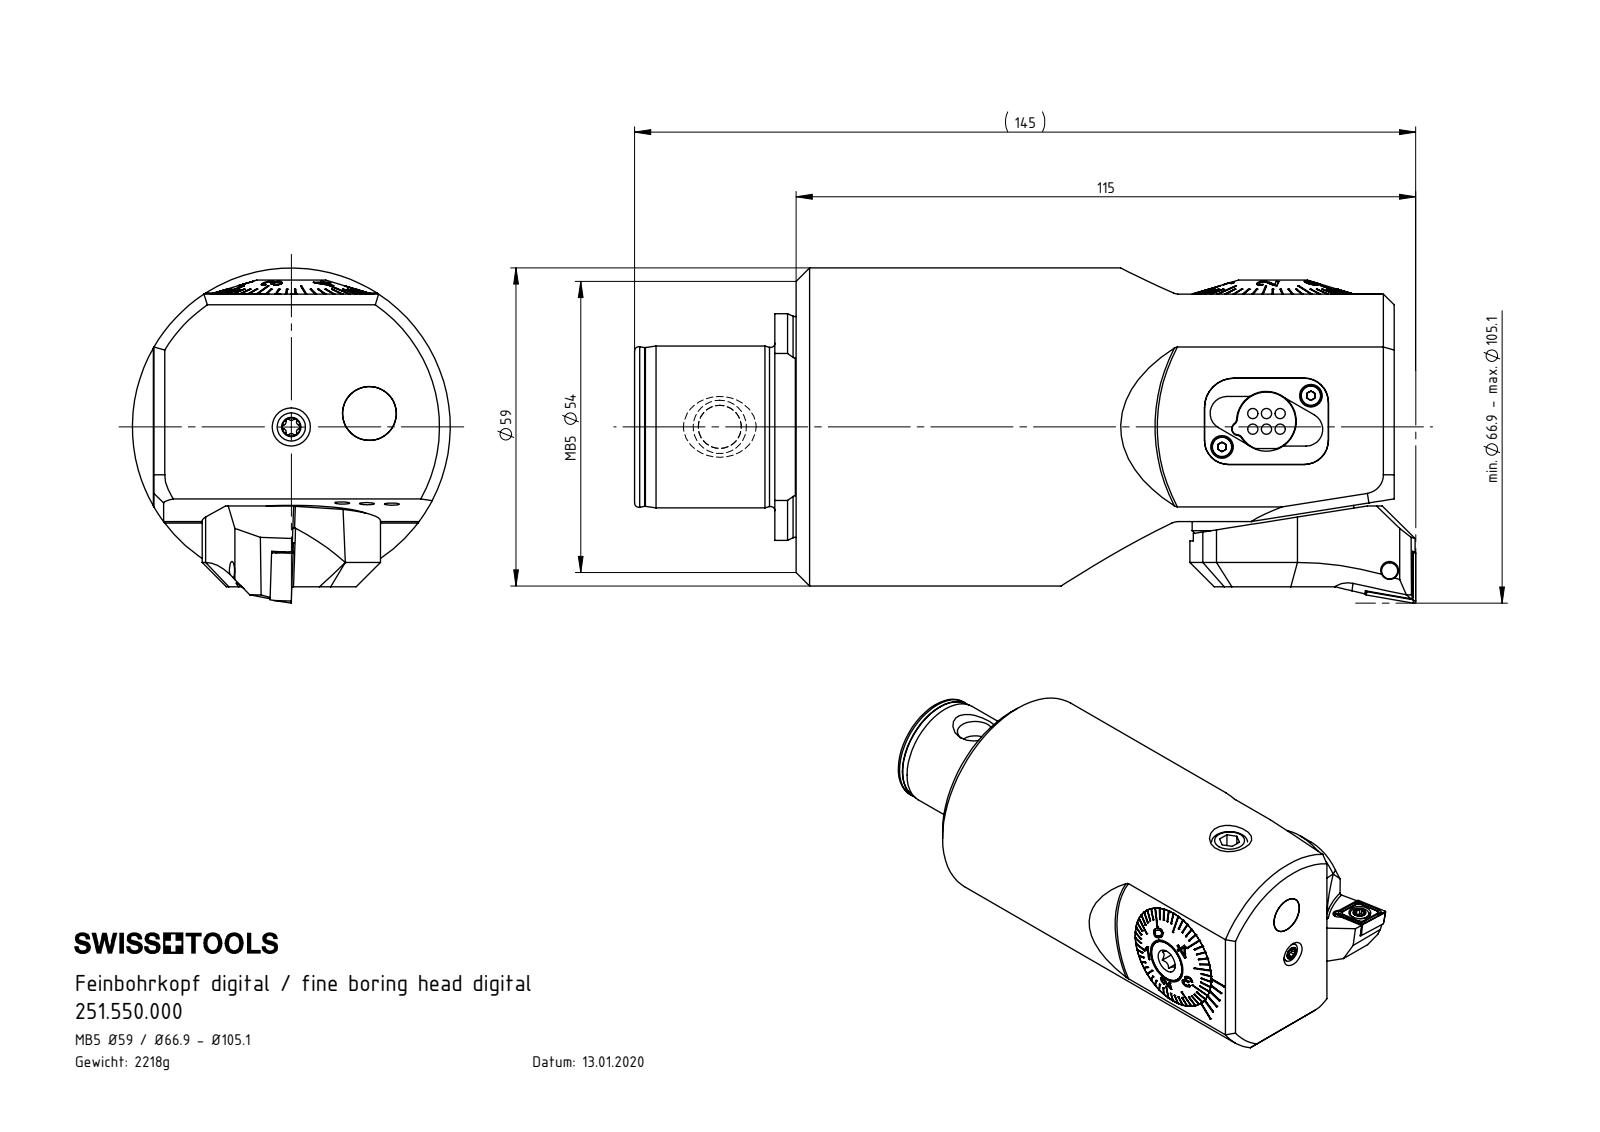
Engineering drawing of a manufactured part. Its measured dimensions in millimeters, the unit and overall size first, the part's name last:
Units: millimetres
Overall size (bounding box): 145 × 65.75 × 55
Round holes (diameter × count): ⌀3.3 ×9, ⌀4.2 ×3, ⌀8.5 ×3, ⌀1.6 ×2, ⌀2.2 ×2, ⌀8 ×2, ⌀4.4 ×1, ⌀5 ×1, ⌀6.1 ×1, ⌀10 ×1, ⌀10.1 ×1, ⌀11 ×1
Round bosses / shafts (diameter × count): ⌀1.9 ×6, ⌀10 ×2, ⌀5.25 ×2, ⌀4 ×2, ⌀3.8 ×2, ⌀2 ×2, ⌀55 ×1, ⌀30 ×1
Partial cylindrical surfaces — rounded edges, fillets, slot ends (radius × count): R0.34 ×12, R0.59 ×12, R1.1 ×9, R1.2 ×8, R4.5 ×5, R0.5 ×4, R3.2 ×3, R4.4 ×3
Main face-to-face distances: 4, 3.7, 111, 8.15, 2, 2.5, 2.8, 47.85, 30, 141
Hole centre spacings: 9.52, 5.73, 5.86, 9.74, 14.5, 19.04, 21, 32.5
Volume: 268 207 mm³ · Surface area: 59 245 mm²
Bodies: 29 solids, 1218 faces (512 planar, 321 cylindrical, 385 other)
Part name (STEP PRODUCT): Fxx-BG7.DA1.0xx_A_F55; Fxx-BG7.DA2.0xx_F55; PEF-DA1.010.032_A; PEF-DA1.011.017_A (+8 more)
STEP written by: SolidWorks 2017 (CONFIG_CONTROL_DESIGN)
